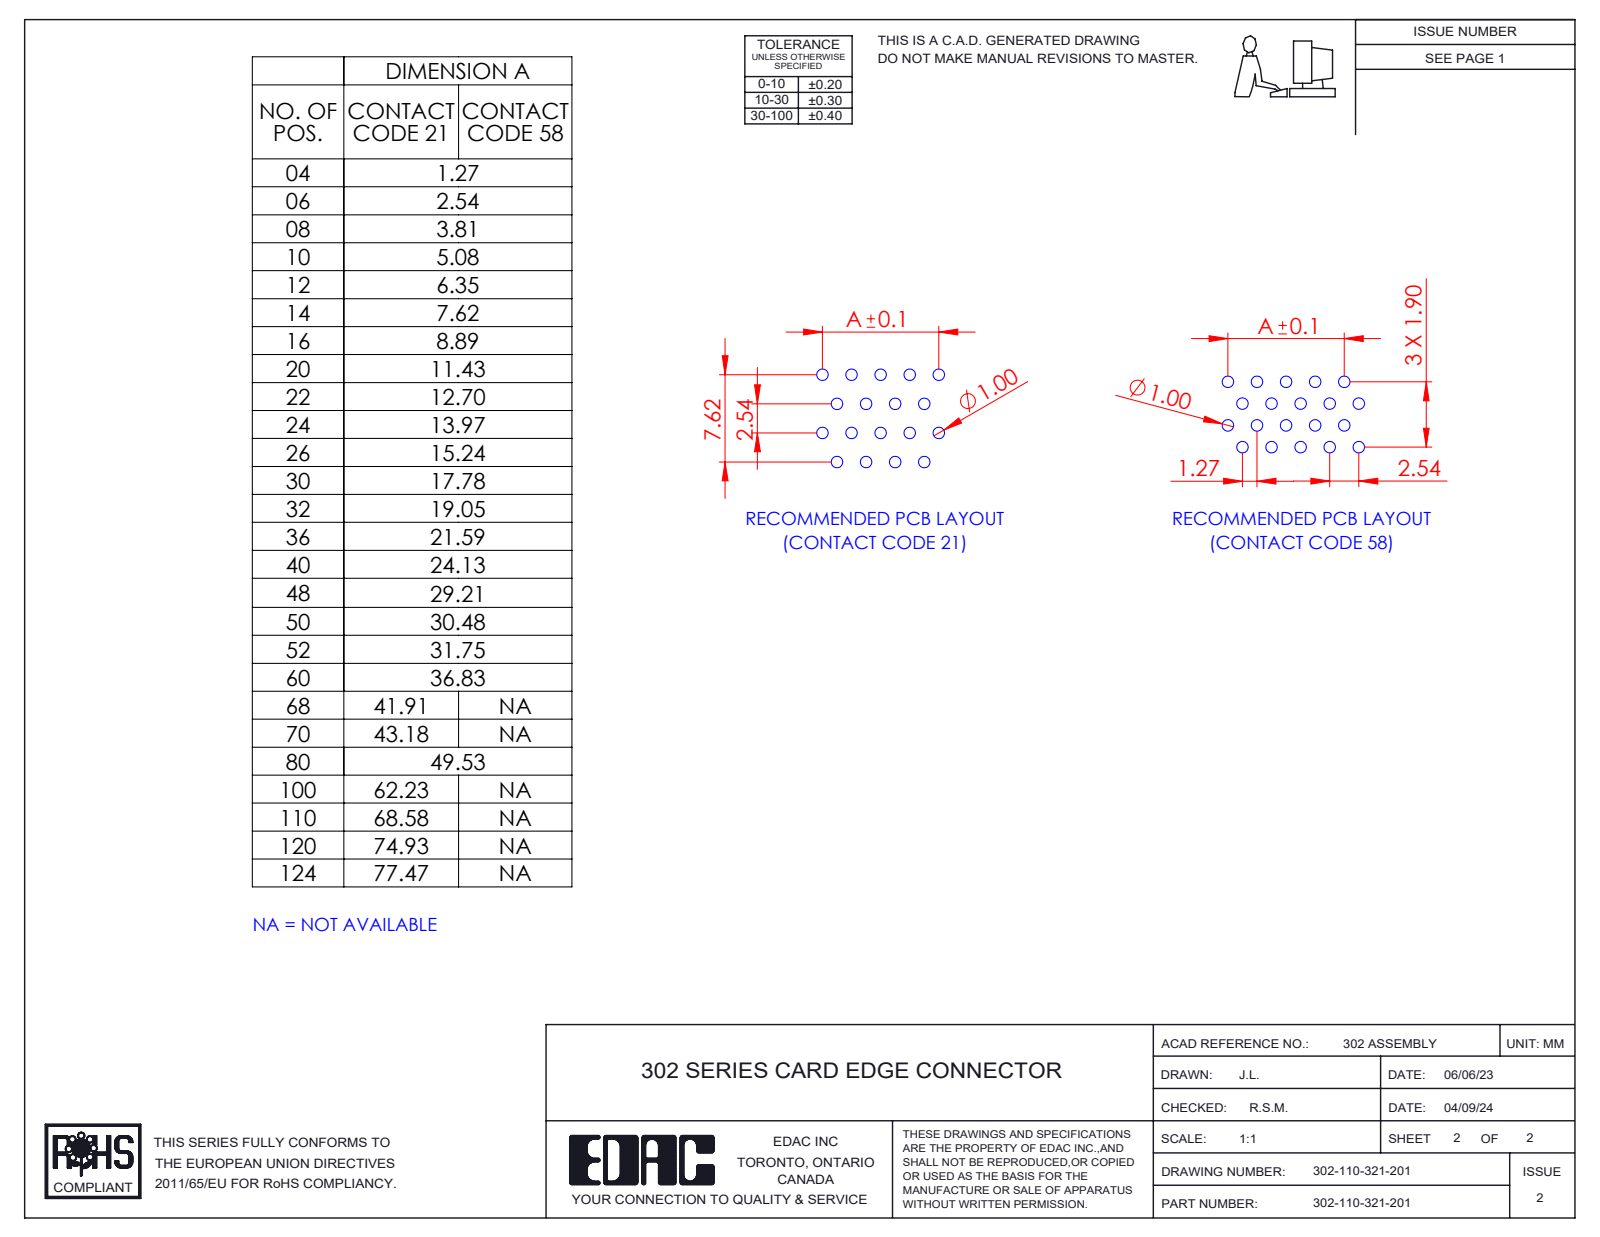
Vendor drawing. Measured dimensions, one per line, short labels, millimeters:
name: 302-110-321-201; Contact_302-290-X21 (1); Contact_302-290-X21 (2); HSG_Vertical HSG
written by: SolidWorks 2023 (CONFIG_CONTROL_DESIGN)
unit: mm
bodies: 111 solids, 5071 faces (3734 planar, 1113 cylindrical, 224 other)
size: 75.95 × 17.63 × 8.88
volume: 5 789 mm³; area: 16 510 mm²
rounds: 118× R0.2, 4× R2.03, 4× R2.09, 2× R0.11, 2× R0.4, 2× R0.41, 2× R1.25, 2× R1.53
face distances: 2.54, 8.88, 1.27, 5.08, 3.81, 7.62, 6.35, 8.89, 10.16, 11.43
